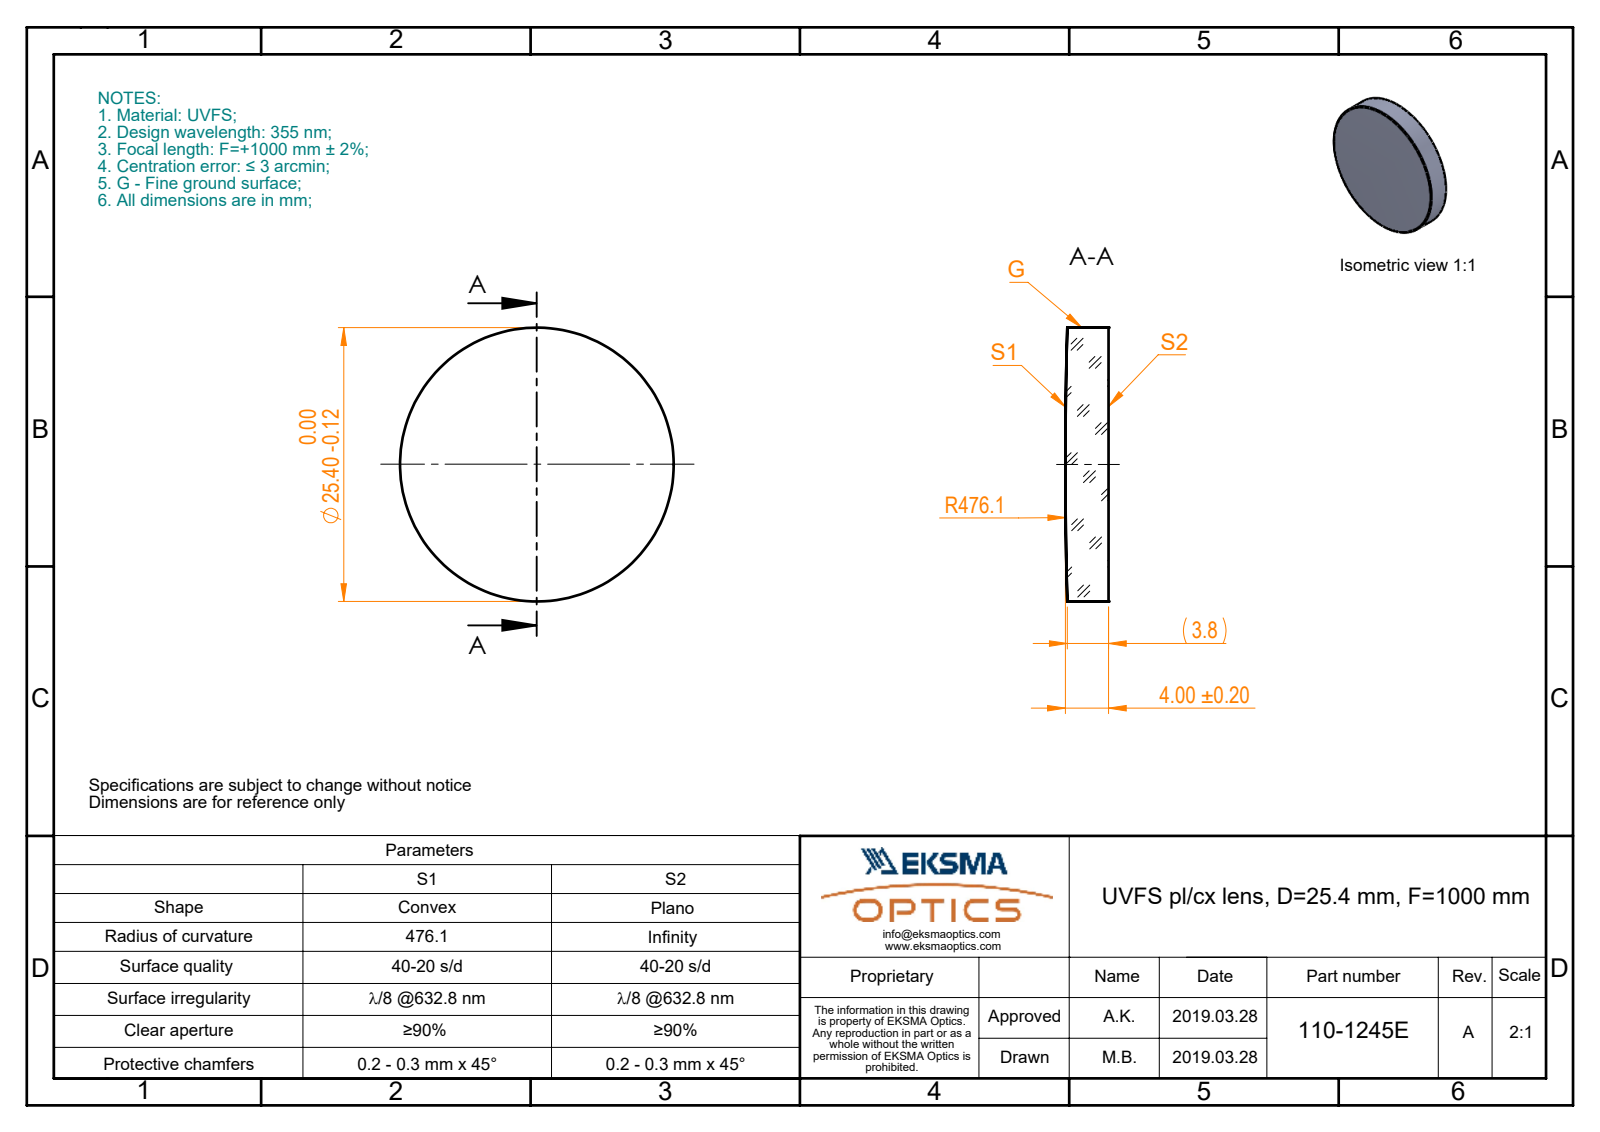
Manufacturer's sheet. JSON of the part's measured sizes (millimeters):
{"part_name": "110-1245E UVFS pl-cx 25.4 F1000", "step_written_by": "SolidWorks 2017 (CONFIG_CONTROL_DESIGN)", "units": "millimeters", "bodies": {"solids": 1, "faces": 5, "planar": 1, "cylindrical": 2, "other": 2}, "overall_size": [25.4, 25.4, 4], "volume_mm3": 1984, "surface_area_mm2": 1319, "round_bosses_or_shafts": [[25.4, 1]]}
